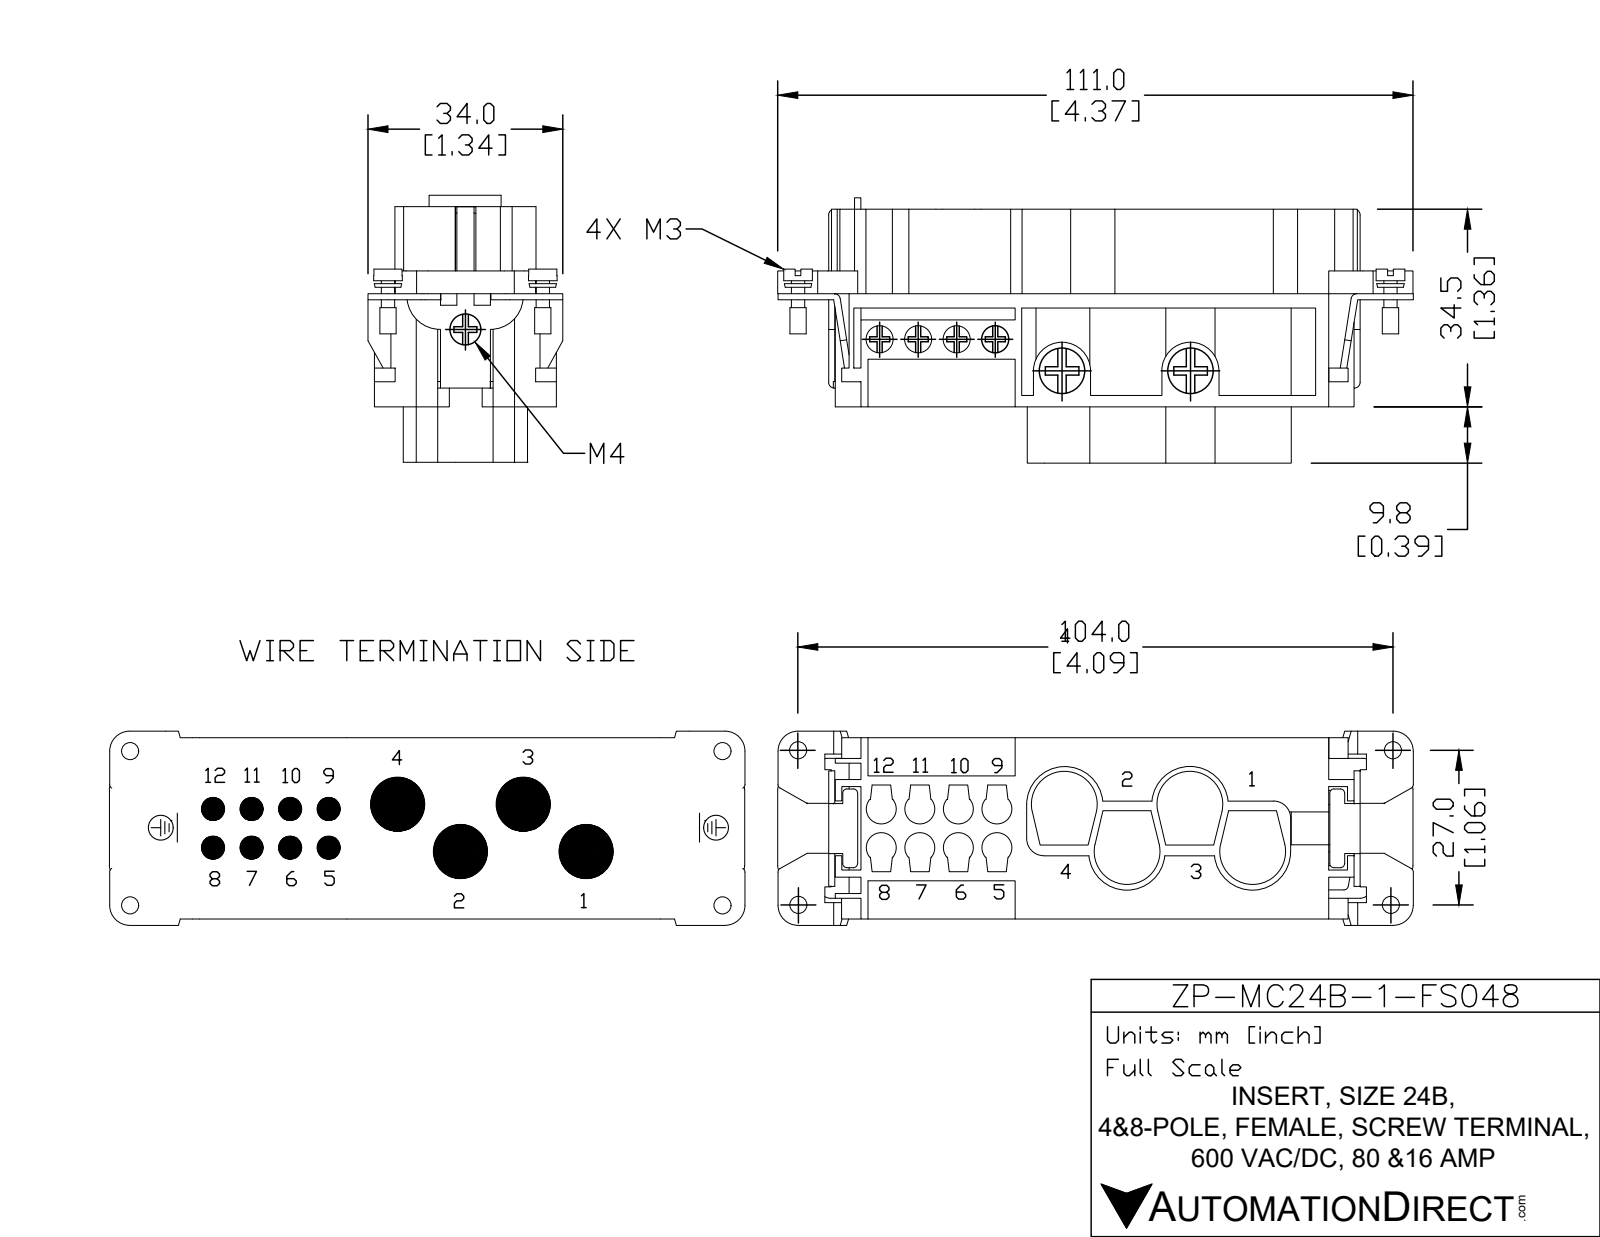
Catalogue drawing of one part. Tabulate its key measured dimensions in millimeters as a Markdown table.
| quantity | value |
| --- | --- |
| part name | ZP-24B-48-FS-INSERT |
| STEP written by | SolidWorks 2011 (AUTOMOTIVE_DESIGN) |
| units | millimeters |
| bodies | 7 solids, 727 faces (574 planar, 149 cylindrical, 4 other) |
| overall size | 111.31 × 46.75 × 34 |
| volume | 43 789 mm³ |
| surface area | 41 038 mm² |
| round holes (diameter × count) | 5.66 × 8, 3.01 × 4, 4.75 × 4, 7.85 × 4, 10.63 × 4, 6.49 × 1, 6.49 × 1, 6.5 × 1, 6.5 × 1 |
| round bosses / shafts (diameter × count) | 5.02 × 4, 2.85 × 4, 2.32 × 4, 2.89 × 1, 2.88 × 1 |
| partial cylindrical surfaces (radius × count) | 0.75 × 18, 1.75 × 10, 2.62 × 8, 1 × 6, 3.5 × 4, 3.75 × 4, 5.51 × 4, 5.75 × 4 |
| main face-to-face distances | 2.5, 17.3, 19.8, 1.05, 6.87, 5.37, 26.37, 15.3, 2, 35.05 |
| hole center spacings | 6.75, 13.5, 9.57, 15.11, 22, 20.25, 11.02, 13.72 |
